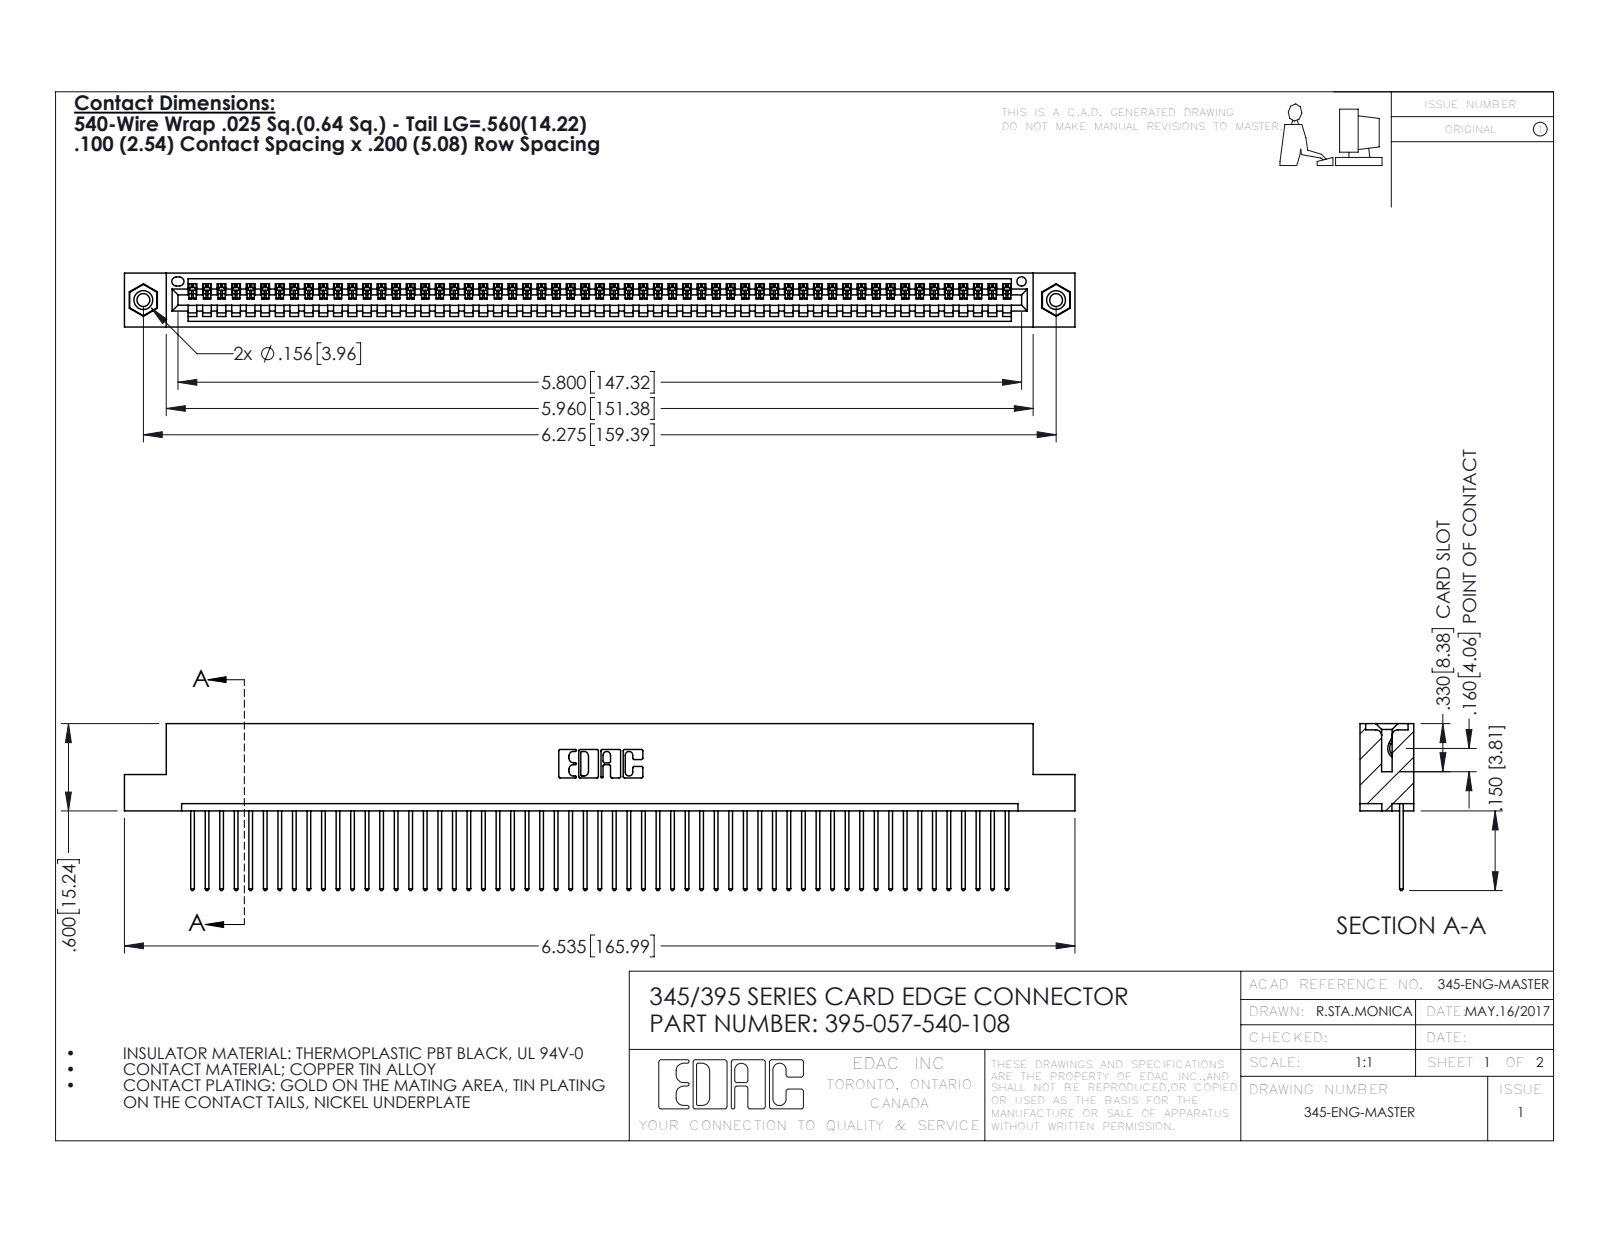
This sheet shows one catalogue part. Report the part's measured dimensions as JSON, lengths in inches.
{"part_name": "345-250-001_345-250-003-102; 345-292-001_345-293-140; 395-057-540-108; 345 Part_Flush Mounting Lugs - 0.156 Dia-TI", "step_written_by": "SolidWorks 2016 (CONFIG_CONTROL_DESIGN)", "units": "inches", "bodies": {"solids": 60, "faces": 3492, "planar": 2392, "cylindrical": 1084, "other": 16}, "overall_size": [6.535, 1.147, 0.37], "volume_in3": 0.974, "surface_area_in2": 34.08, "round_holes": [[0.089, 2], [0.125, 2], [0.156, 2], [0.064, 1]], "round_bosses_or_shafts": [[0.155, 2]], "partial_cylinders_radius": [[0.006, 114], [0.01, 114], [0.01, 22], [0.007, 6], [0.031, 6], [0.026, 3], [0.031, 2], [0.04, 2]], "face_to_face_distances": [0.072, 0.298, 0.37, 0.098, 0.272, 0.025, 0.2, 0.225, 0.149, 0.072], "hole_center_spacings": [0.27, 6.039, 6.275]}
